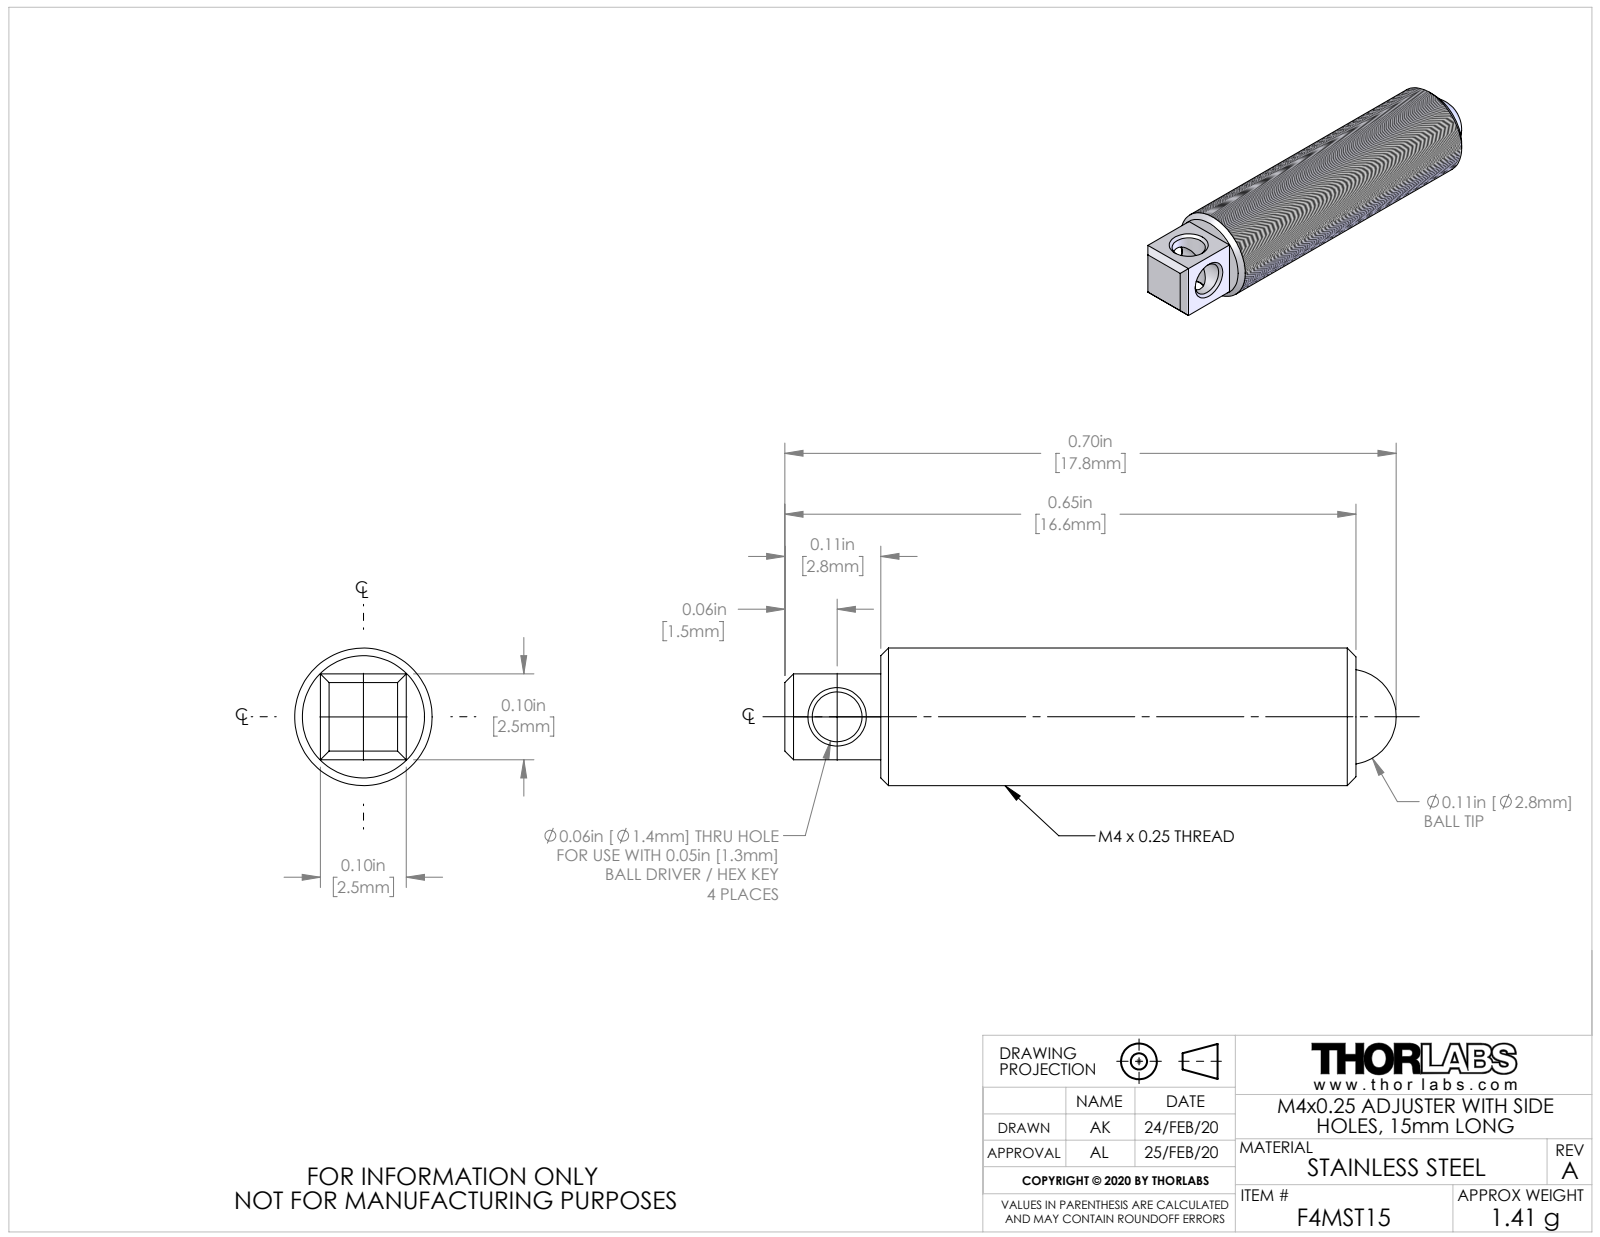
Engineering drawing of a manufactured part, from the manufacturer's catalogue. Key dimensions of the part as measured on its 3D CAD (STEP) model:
Part name (STEP PRODUCT): TTN203601-E0W
STEP written by: SolidWorks 2018 (AUTOMOTIVE_DESIGN)
Units: inches
Bodies: 2 solids, 41 faces (11 planar, 12 cylindrical, 18 other)
Overall size (bounding box): 0.701 × 0.157 × 0.157
Volume: 0.011 in³ · Surface area: 0.406 in²
Round holes (diameter × count): ⌀0.057 ×2, ⌀0.11 ×1
Round bosses / shafts (diameter × count): ⌀0.157 ×1
Main face-to-face distances: 0.098, 0.11, 0.545, 0.655
